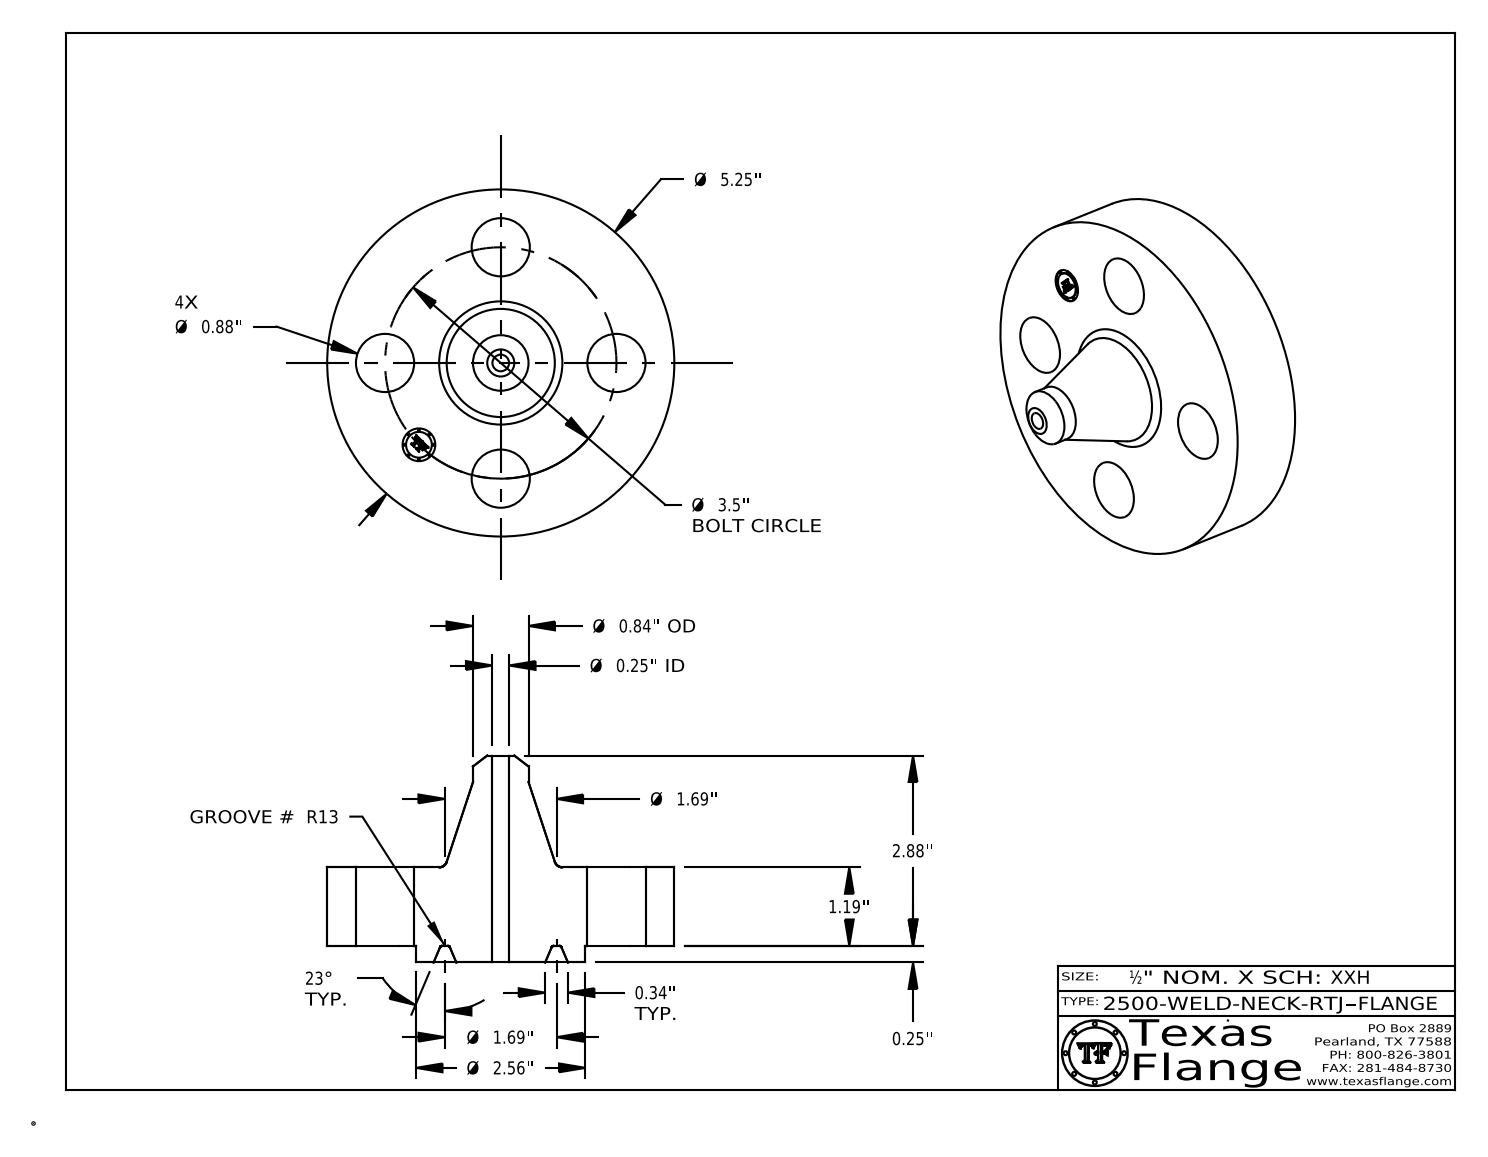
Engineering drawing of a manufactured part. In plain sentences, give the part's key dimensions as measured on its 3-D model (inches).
The part is named "2500-WELD-NECK-RTJ". Its 3-D file was written by "CATIA V5 STEP AP214 (AUTOMOTIVE_DESIGN)". It is 1 solid with 421 faces: 371 planar, 36 cylindrical and 14 other. Overall it measures 5.25 by 5.25 by 3.13 inches. Its volume is 25.55 cubic inches and its surface area 81.72 square inches. Round holes: 4 of diameter 0.88, 1 of diameter 0.252, 1 of diameter 0.495. Round bosses or shafts: 8 of diameter 0.03, 1 of diameter 5.25, 1 of diameter 2.563, 1 of diameter 0.84, 1 of diameter 0.39. The main face-to-face distances are 1.19, 0.25, 1.44, 3.13, 2.88, 1.69, 1.425, 1.175, 0.015, 1.705. The hole center spacings are 1.75, 2.475, 1.339, 3.233, 3.5.
